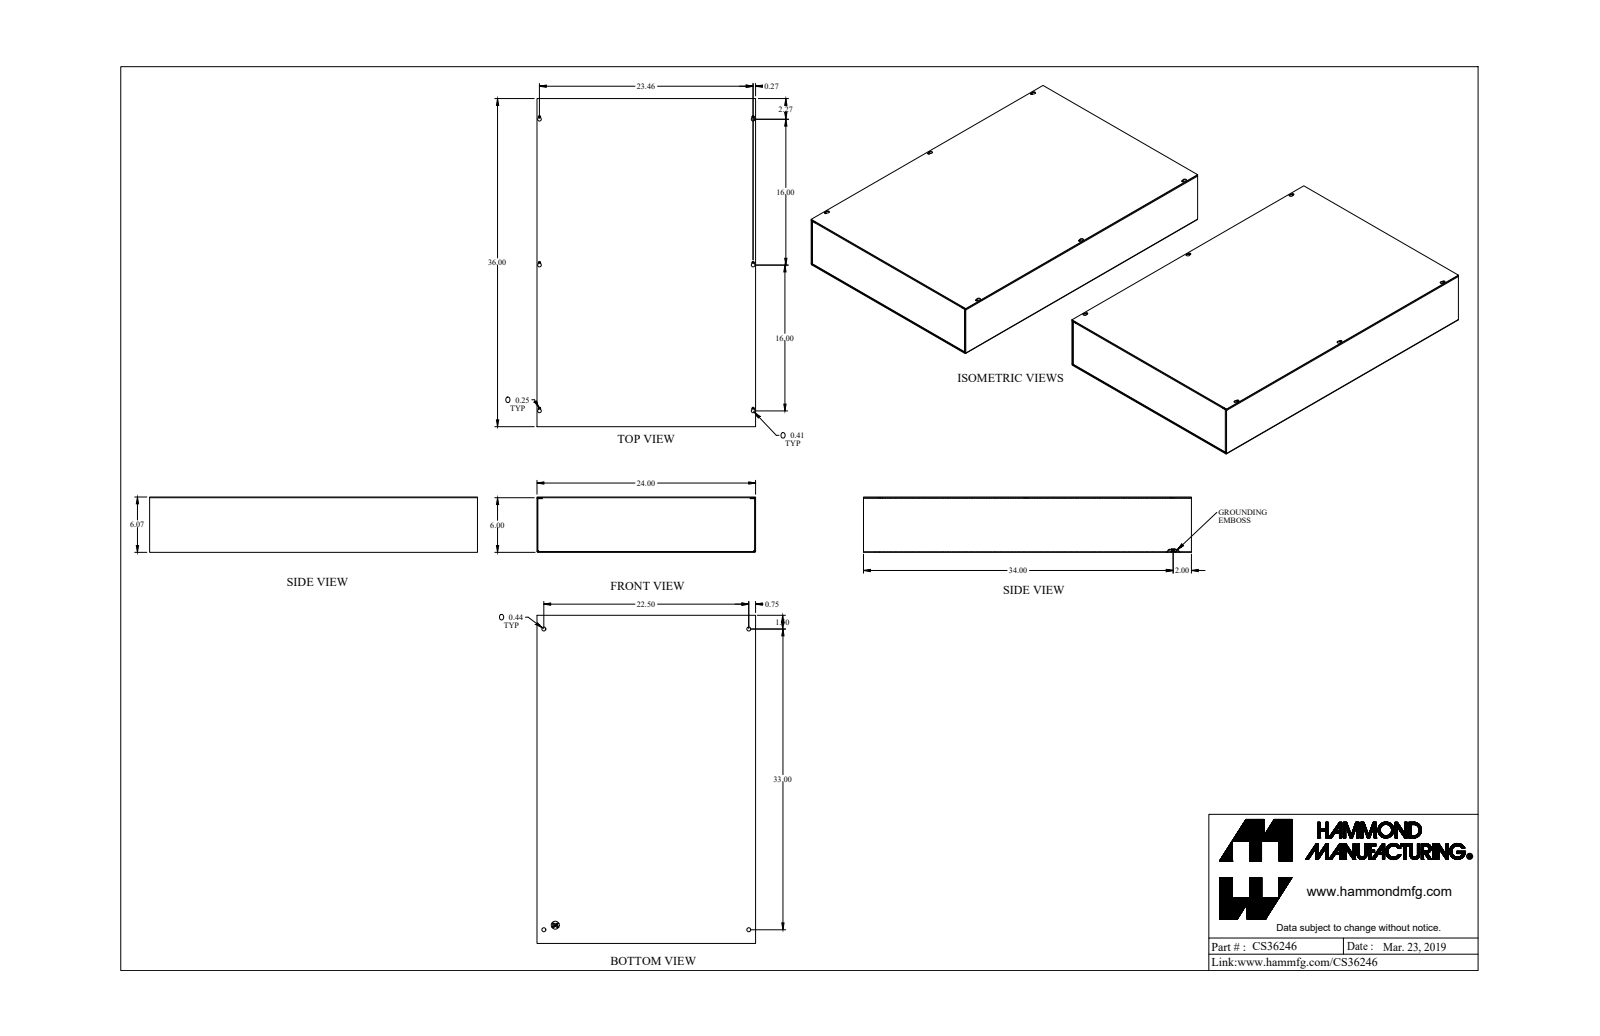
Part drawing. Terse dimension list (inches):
name: CS36246_Default
written by: SolidWorks 2019 (CONFIG_CONTROL_DESIGN)
unit: in
bodies: 4 solids, 221 faces (129 planar, 84 cylindrical, 8 other)
size: 36 × 24 × 6.072
volume: 181.2 in³; area: 5 063 in²
holes: 7× ⌀0.17, 4× ⌀0.437, 1× ⌀0.5
bosses: 1× ⌀0.492, 1× ⌀0.314
rounds: 12× R0.036, 12× R0.108, 8× R0.072, 6× R0.125, 6× R0.203
face distances: 0.072, 6, 5.928, 6.072, 23.928, 35.928, 24, 23.856, 36, 35.856
hole spacings: 0.693, 16, 16.507, 22.985, 28.29, 28.396, 32.504, 39.804
